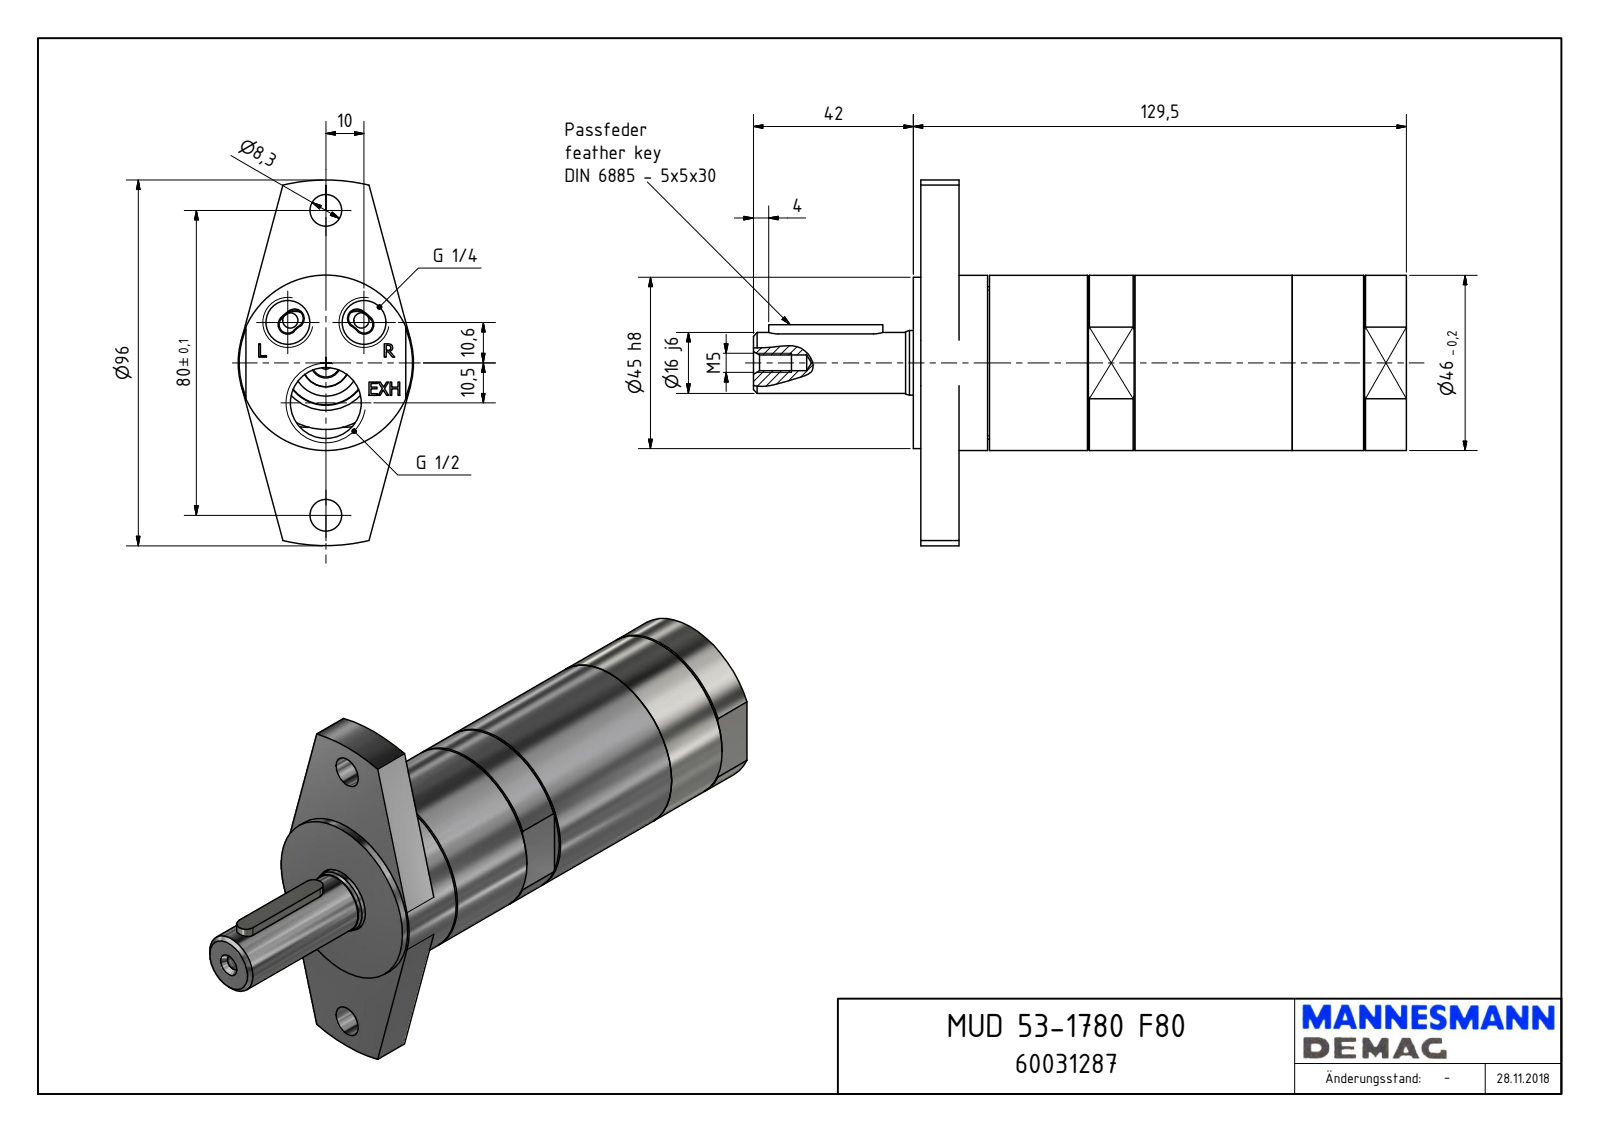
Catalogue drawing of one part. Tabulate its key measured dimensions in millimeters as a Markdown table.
| quantity | value |
| --- | --- |
| part name | MUD 53-1780 F80_60031287 |
| STEP written by | Autodesk Inventor 2018 (AUTOMOTIVE_DESIGN) |
| units | millimeters |
| bodies | 1 solid, 164 faces (99 planar, 34 cylindrical, 31 other) |
| overall size | 171.5 × 96 × 46 |
| volume | 232 968 mm³ |
| surface area | 33 165 mm² |
| round holes (diameter × count) | 8.3 × 2, 11.45 × 2, 4.13 × 1, 17.5 × 1, 18.63 × 1, 21.5 × 1, 23 × 1 |
| round bosses / shafts (diameter × count) | 46 × 1, 45 × 1, 40 × 1, 19.56 × 1, 16.95 × 1, 16 × 1 |
| partial cylindrical surfaces (radius × count) | 2.5 × 2, 5 × 2, 17.29 × 1, 19 × 1, 48 × 1 |
| main face-to-face distances | 10, 12, 2, 129.5, 127.5, 117.5, 42, 46, 8, 109.5 |
| hole center spacings | 14.57, 23.35, 31.05, 40, 51.58, 10.5, 20, 29.5 |
